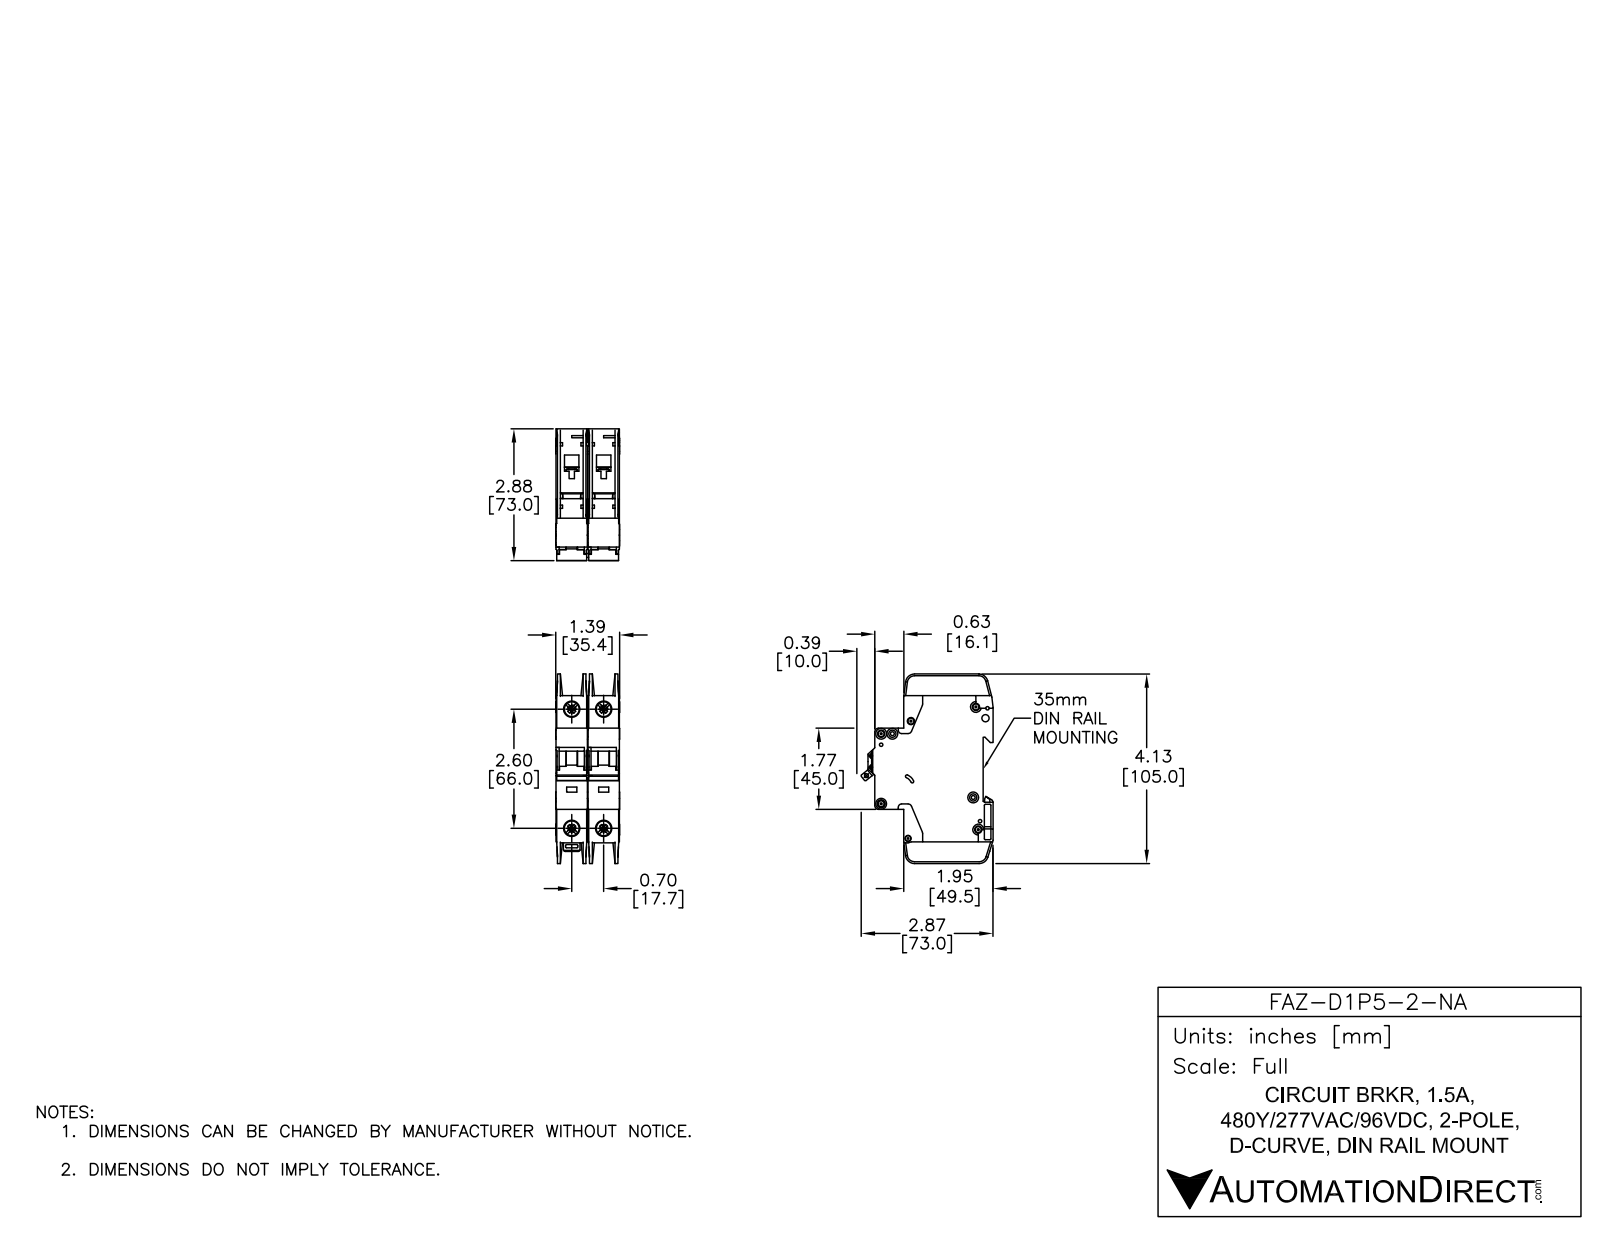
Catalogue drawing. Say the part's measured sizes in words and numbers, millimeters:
The part is named "FAZ-D1P5-2-NA". Its 3-D file was written by "SolidWorks 2014 (AUTOMOTIVE_DESIGN)". It is 6 solids with 1568 faces: 818 planar, 526 cylindrical and 224 other. Overall it measures 105 by 73.04 by 35.4 millimeters. Its volume is 155 390 cubic millimeters and its surface area 49 479 square millimeters. Round holes: 7 of diameter 3.6, 4 of diameter 7.15, 4 of diameter 8.2, 2 of diameter 1.09, 2 of diameter 1.5, 2 of diameter 4, 1 of diameter 1.9, 1 of diameter 2.15, 1 of diameter 2.2, 1 of diameter 2.55, 1 of diameter 3.3, 1 of diameter 3.4. Round bosses or shafts: 7 of diameter 6, 2 of diameter 2.5. Partial cylindrical surfaces (rounded edges, fillets, slot ends): 47 of radius 0.25, 24 of radius 0.5, 18 of radius 1, 12 of radius 2, 5 of radius 5, 4 of radius 1.8, 4 of radius 4, 2 of radius 0.2. The main face-to-face distances are 17.7, 17.5, 0.7, 15.05, 2.45, 1.75, 15.75, 13.3, 35.2, 17. The hole center spacings are 6.2, 17.7, 66, 68.33, 5.19, 6.1, 8.19, 8.56.
